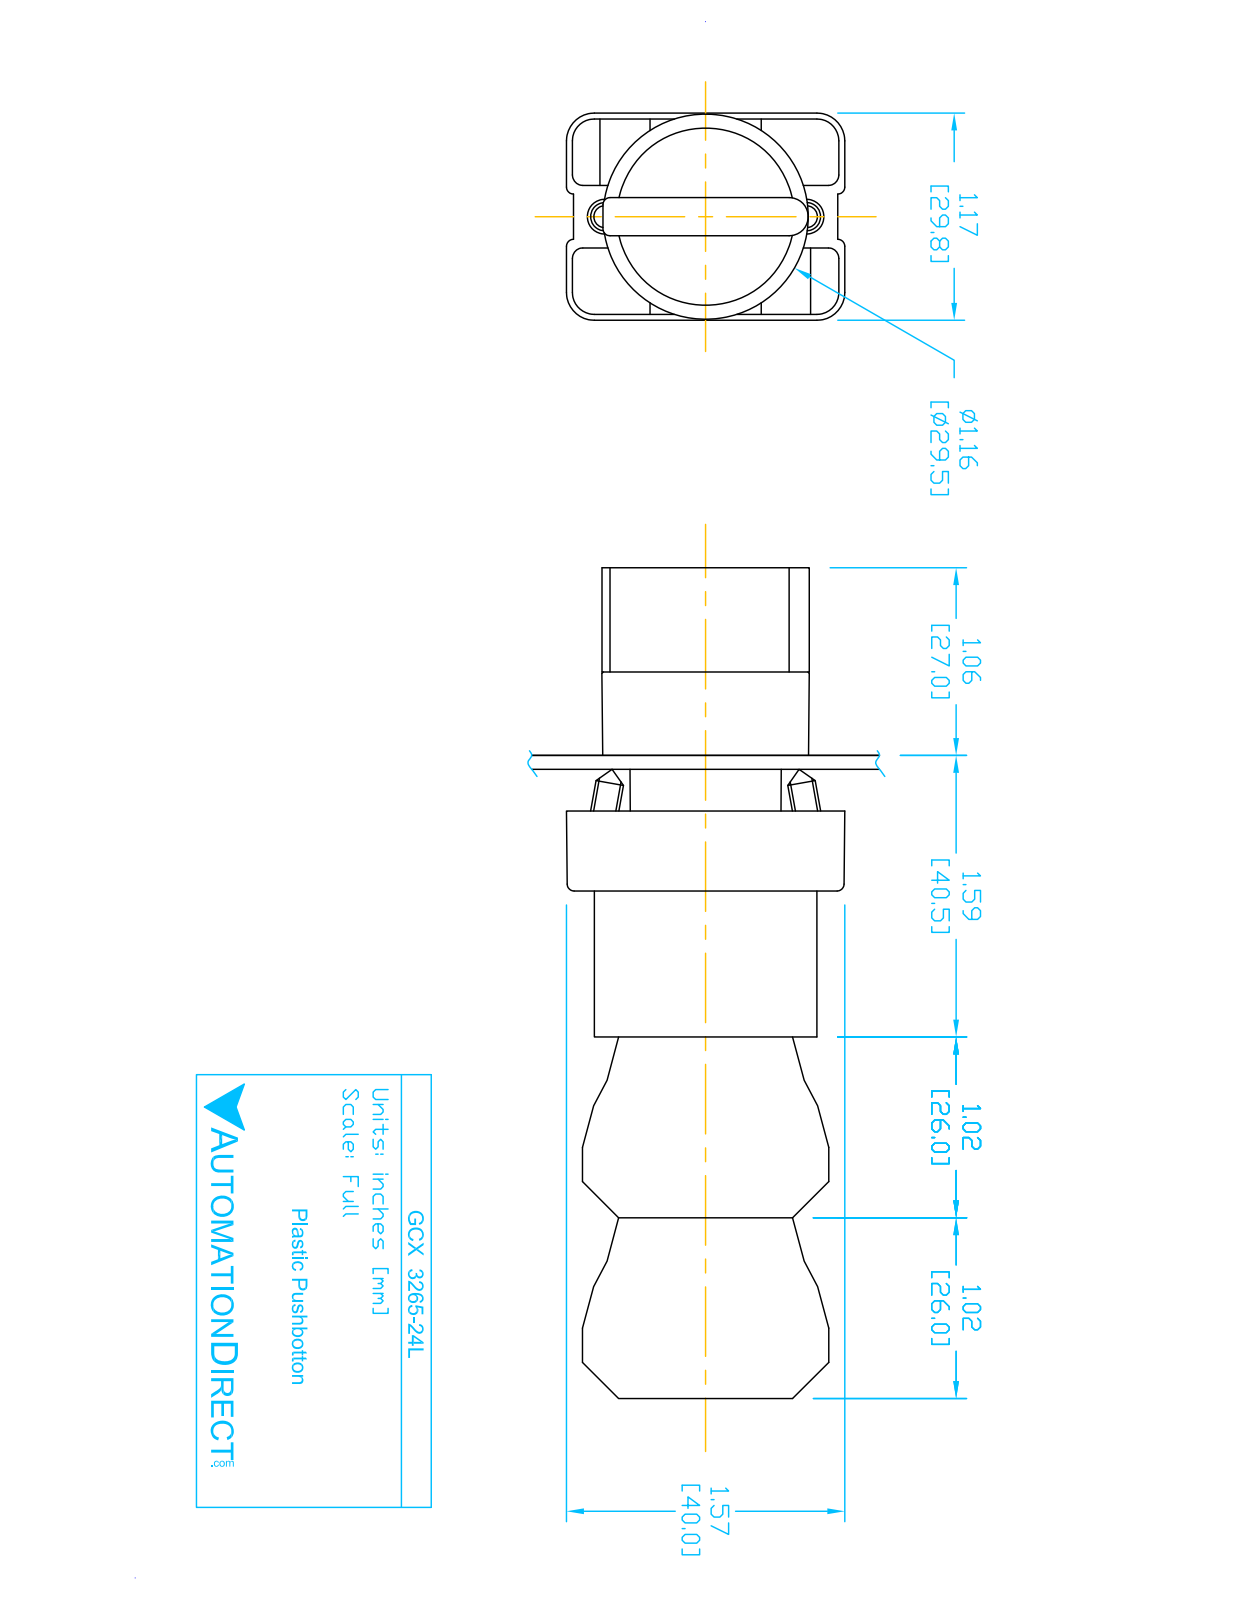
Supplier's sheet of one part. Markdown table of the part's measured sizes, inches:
| quantity | value |
| --- | --- |
| part name | ecx1040; GCX3265-24L; ECX3029-2; ecx1030 (+2 more) |
| STEP written by | SolidWorks 2016 (AUTOMOTIVE_DESIGN) |
| units | inches |
| bodies | 11 solids, 724 faces (488 planar, 193 cylindrical, 43 other) |
| overall size | 4.677 × 1.581 × 1.177 |
| volume | 4.751 in³ |
| surface area | 59.22 in² |
| round holes (diameter × count) | 0.079 × 4, 0.087 × 2, 0.124 × 2, 0.13 × 2, 0.197 × 1, 0.469 × 1, 0.878 × 1, 0.888 × 1, 1.024 × 1 |
| round bosses / shafts (diameter × count) | 0.157 × 4, 1.175 × 1, 1.004 × 1, 0.945 × 1, 0.856 × 1, 0.78 × 1, 0.504 × 1 |
| partial cylindrical surfaces (radius × count) | 0.059 × 24, 0.041 × 12, 0.124 × 12, 0.157 × 12, 0.039 × 9, 0.02 × 2, 0.063 × 2, 0.079 × 2 |
| main face-to-face distances | 0.579, 0.593, 1.024, 1.171, 0.014, 0.827, 1.85, 3.043, 2.02, 1.193 |
| hole center spacings | 0.236, 1.003, 0.974, 0.472, 0.539, 0.544, 1.083, 0.484 |
